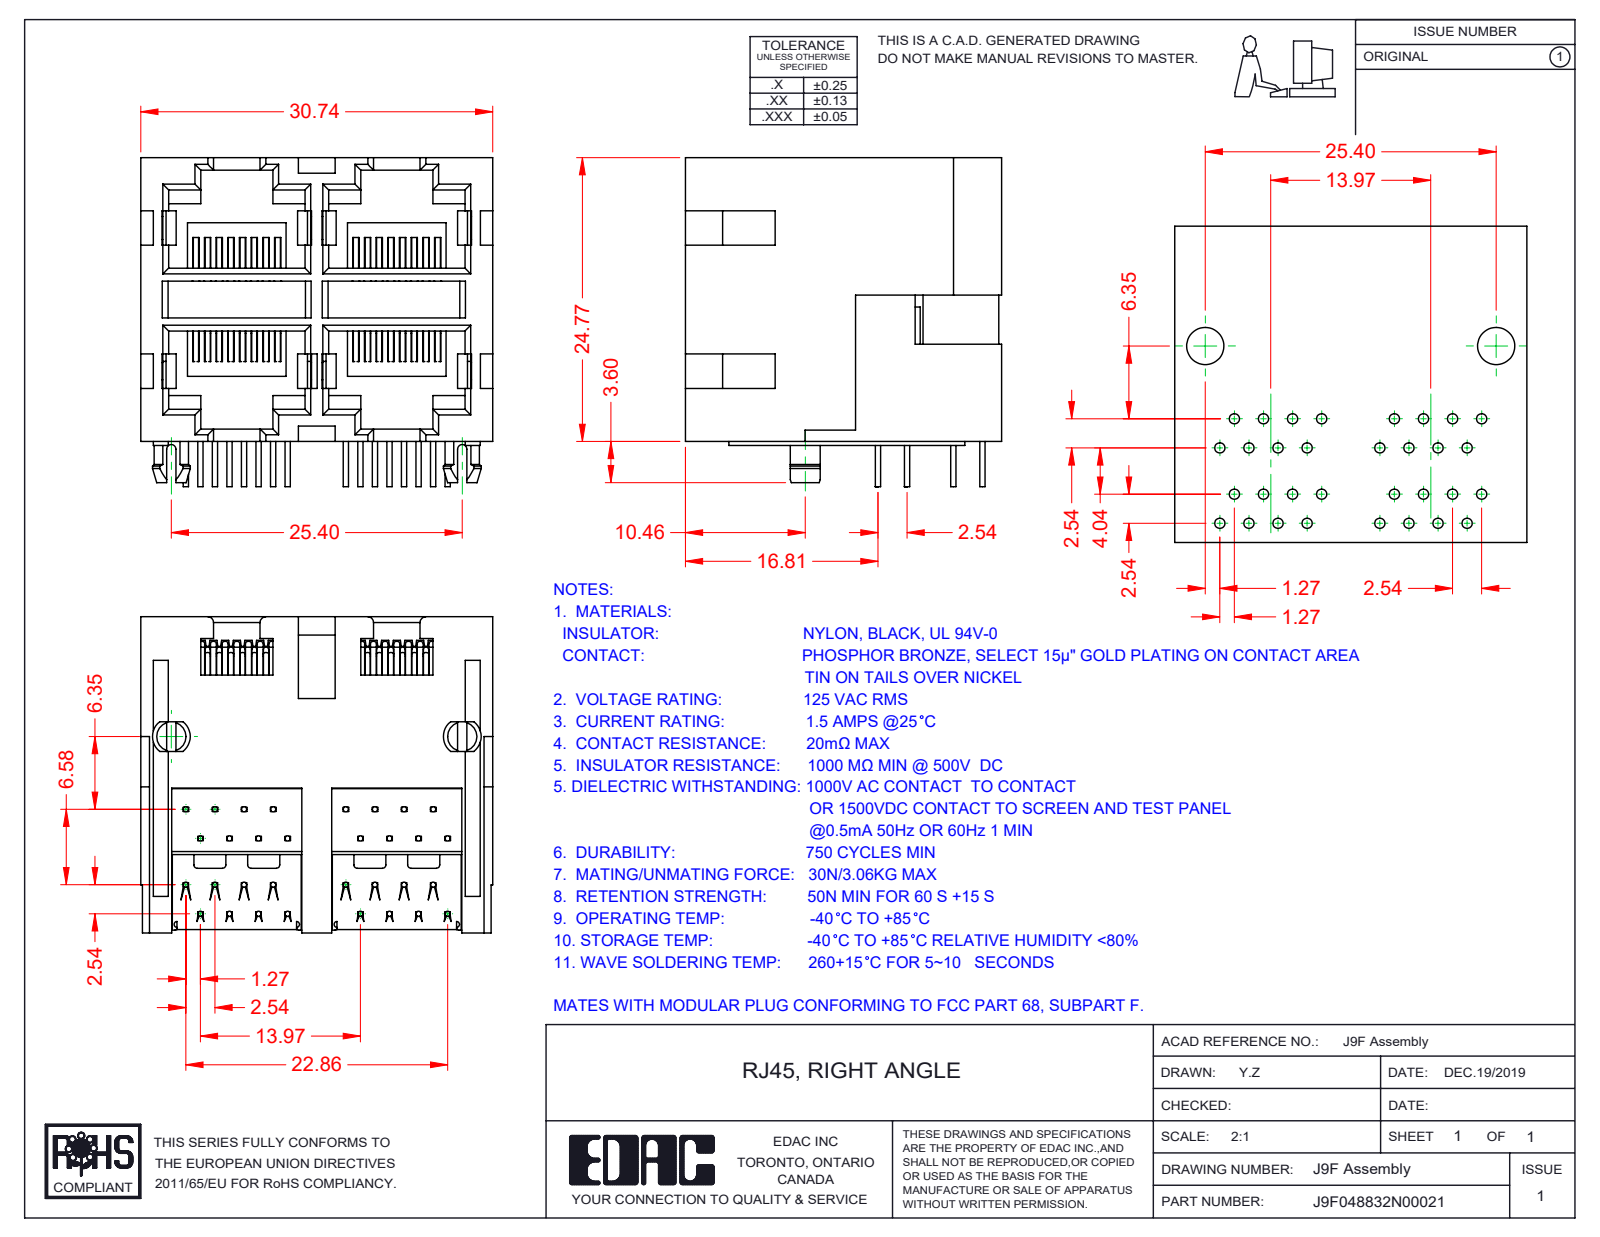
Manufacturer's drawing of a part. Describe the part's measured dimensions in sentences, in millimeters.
The part is named "9F Contact Lock Upper; RJ9F048832N00021; 9F Contacts Upper; 9F Contacts Lower (+2 more)". Its 3-D file was written by "SolidWorks 2016 (CONFIG_CONTROL_DESIGN)". It is 37 solids with 2810 faces: 1899 planar, 557 cylindrical and 354 other. Overall it measures 30.74 by 28.71 by 27.6 millimeters. Its volume is 11 763 cubic millimeters and its surface area 19 774 square millimeters. Round bosses or shafts: 144 of diameter 0.46. Partial cylindrical surfaces (rounded edges, fillets, slot ends): 63 of radius 0.2, 25 of radius 0.5, 9 of radius 0.3, 4 of radius 0.25, 2 of radius 0.4, 2 of radius 0.45, 2 of radius 1.5, 2 of radius 1.65. The main face-to-face distances are 13.97, 1, 0.35, 12.7, 15, 13.05, 11.98, 1.05, 13.62, 5.5.
